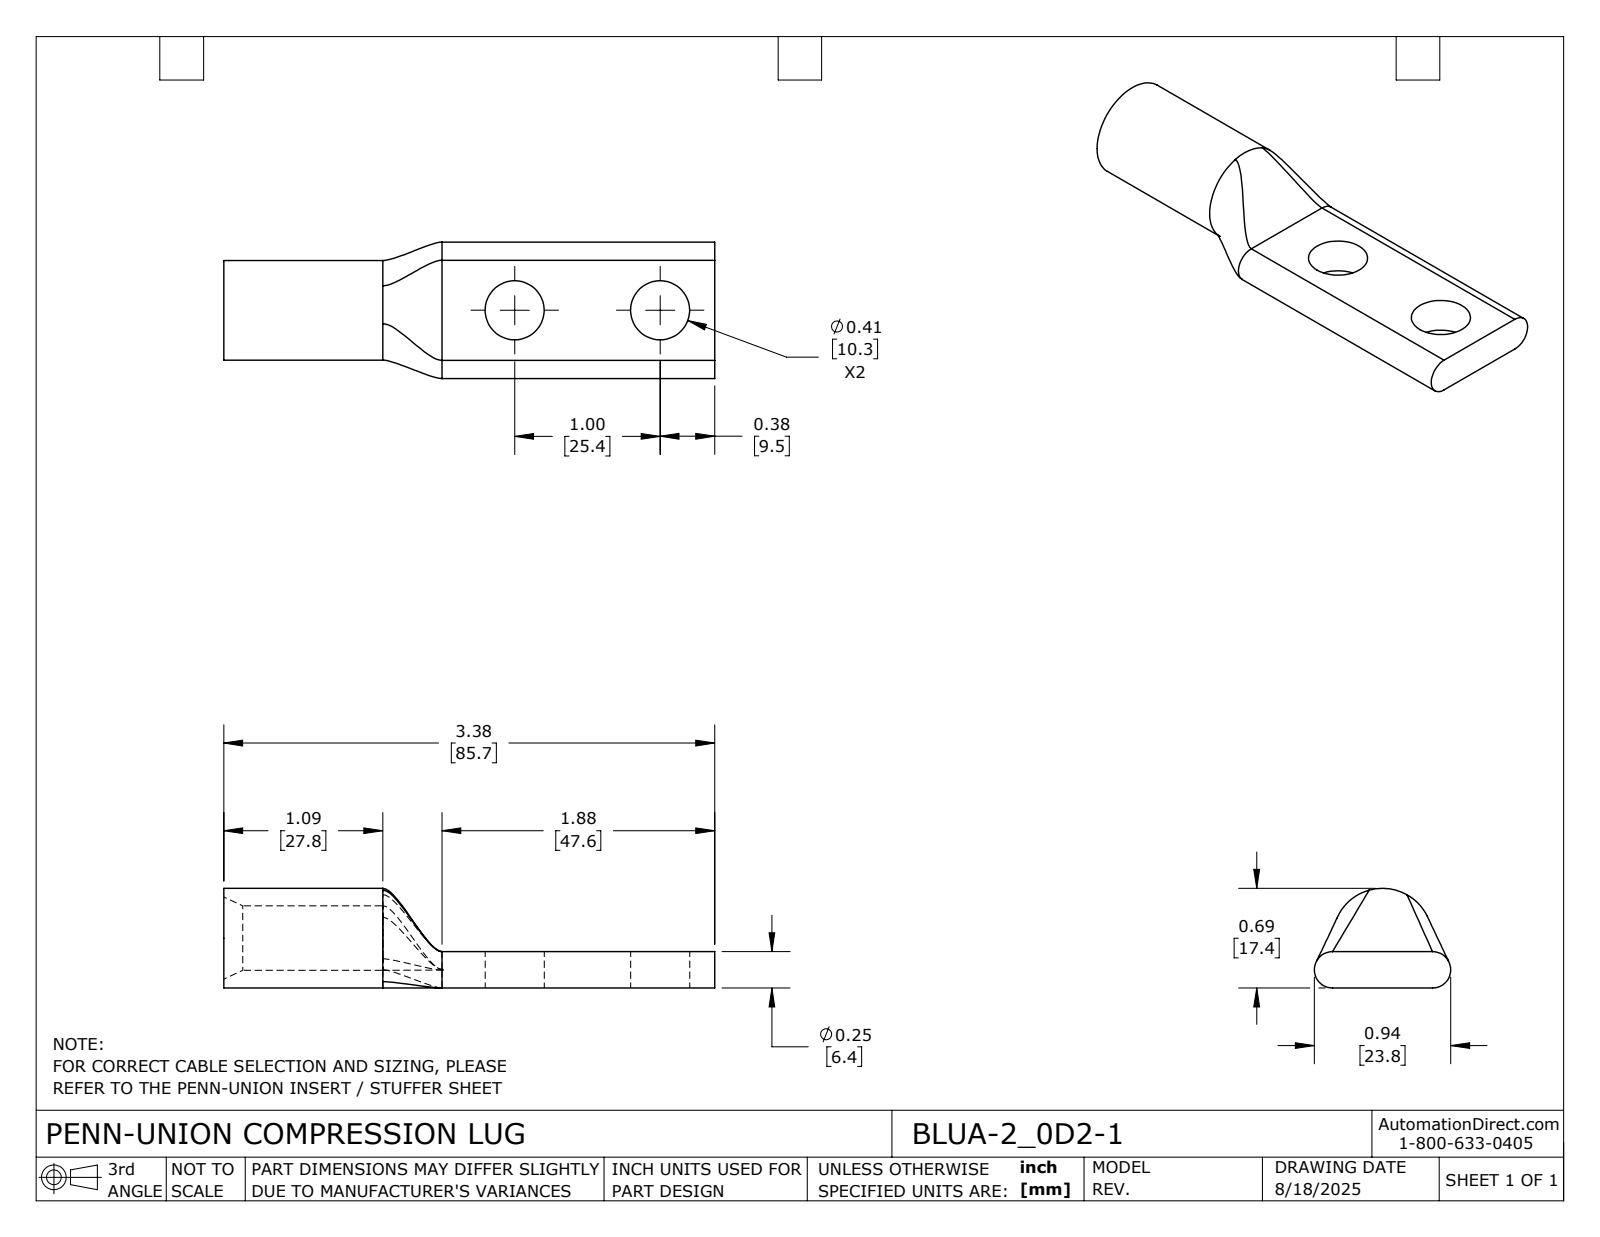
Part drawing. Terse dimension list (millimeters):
name: BLUA-2_0D2-1
written by: SolidWorks 2024 (CONFIG_CONTROL_DESIGN)
unit: mm
bodies: 1 solid, 26 faces (5 planar, 11 cylindrical, 10 other)
size: 85.7 × 23.8 × 17.4
volume: 10 900 mm³; area: 6 510 mm²
holes: 2× ⌀10.3, 1× ⌀11.3
bosses: 1× ⌀17.4
rounds: 2× R3.2
face distances: 6.4, 85.7, 38.1, 47.6
hole spacings: 25.4
